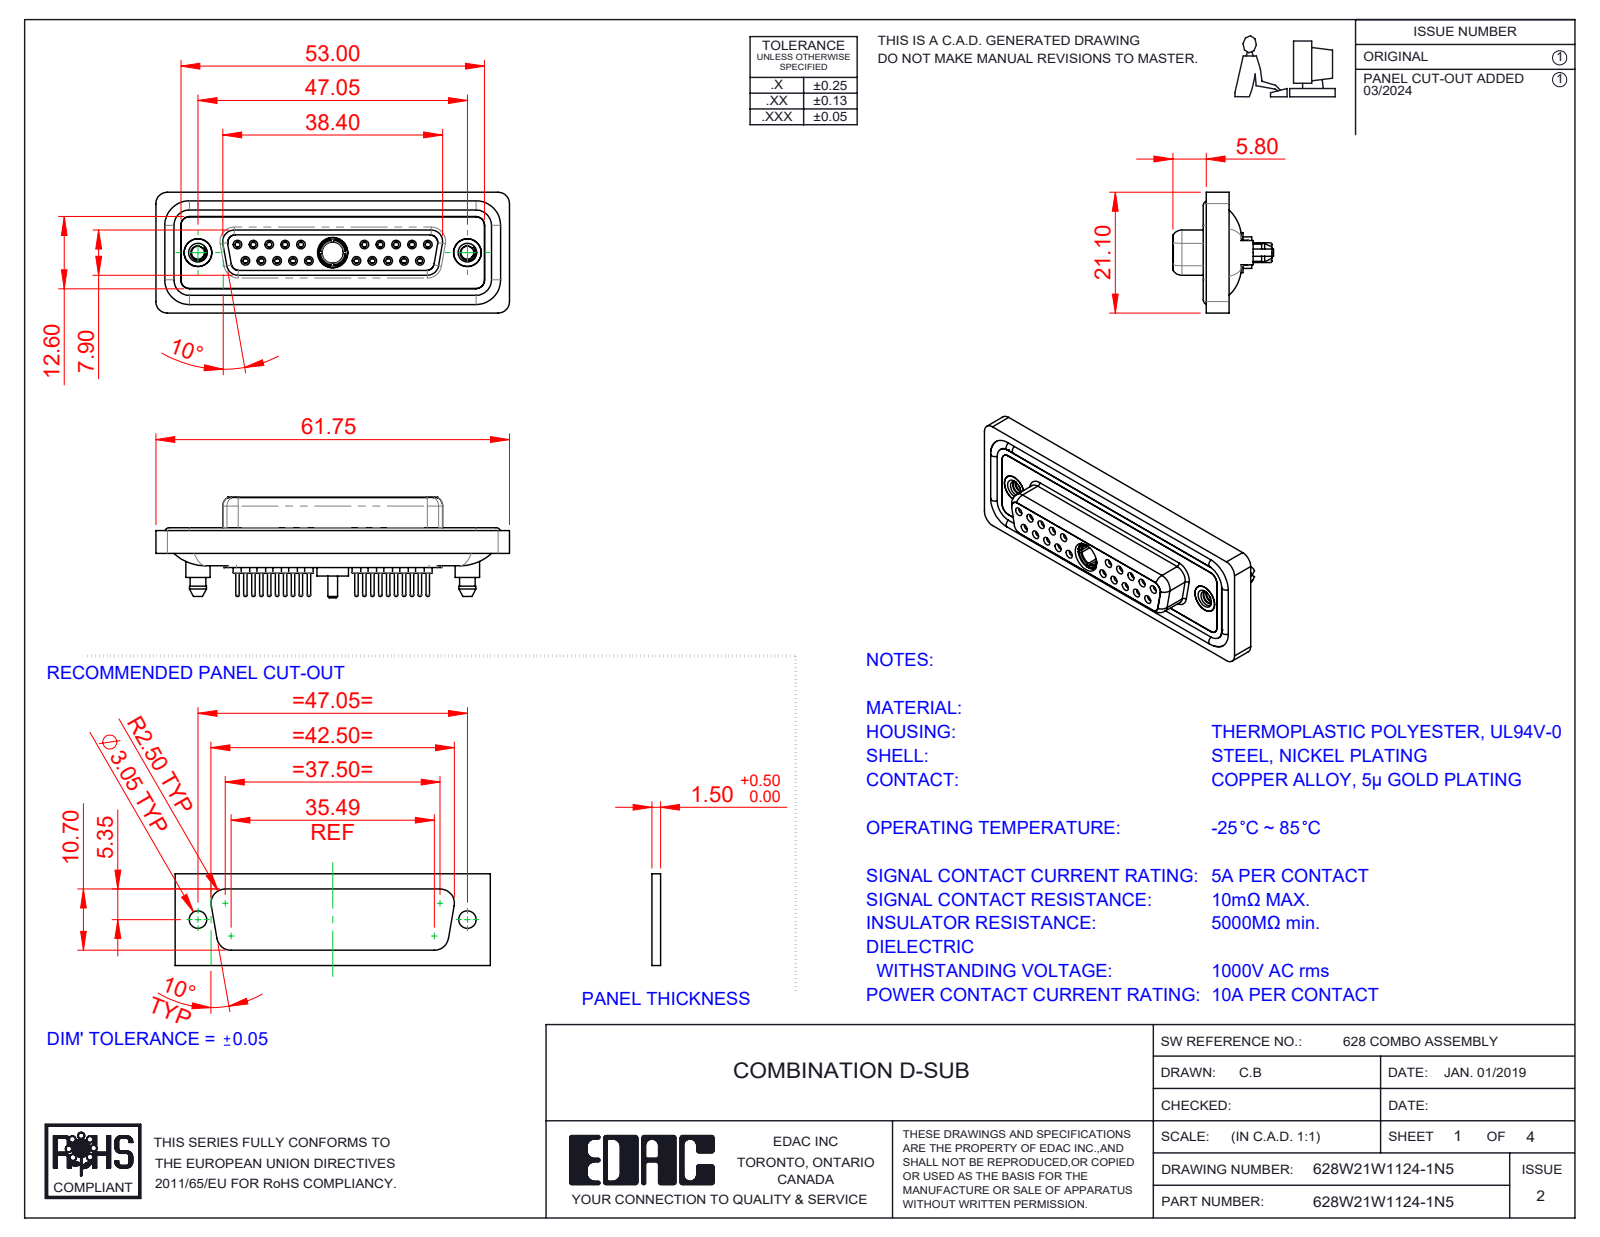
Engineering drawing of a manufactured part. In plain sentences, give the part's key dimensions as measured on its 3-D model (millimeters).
The part is named "628Combo Contact Row 1_24; 628Combo Waterproof Housing_25 Contacts; 628Combo Housing_21W1; 628W21W1124-1N5 (+5 more)". Its 3-D file was written by "SolidWorks 2023 (CONFIG_CONTROL_DESIGN)". It is 29 solids with 1610 faces: 450 planar, 623 cylindrical and 537 other. Overall it measures 61.75 by 21.1 by 17.55 millimeters. Its volume is 8 493 cubic millimeters and its surface area 14 322 square millimeters. Round holes: 20 of diameter 0.9, 20 of diameter 1.1, 20 of diameter 1.5, 20 of diameter 2, 10 of diameter 1.6, 10 of diameter 1.7, 3 of diameter 4.85, 2 of diameter 2.26, 2 of diameter 4, 2 of diameter 4.05, 2 of diameter 5, 1 of diameter 3.7. Round bosses or shafts: 20 of diameter 2.2, 20 of diameter 0.6, 14 of diameter 1.6, 2 of diameter 5.4, 2 of diameter 4.95, 2 of diameter 4.8, 2 of diameter 4.25, 1 of diameter 5.5. Partial cylindrical surfaces (rounded edges, fillets, slot ends): 24 of radius 1.5, 18 of radius 2, 10 of radius 1.6, 8 of radius 1.35, 4 of radius 0.25, 4 of radius 0.5, 4 of radius 0.6, 4 of radius 0.65. The main face-to-face distances are 0.4, 1.8, 7.45, 6.6, 5.65, 1.6, 0.5, 7.05, 2.9, 1.1. The hole center spacings are 3.16, 2.77, 5.54, 5.03, 8.31, 7.48, 16.62, 19.39.
